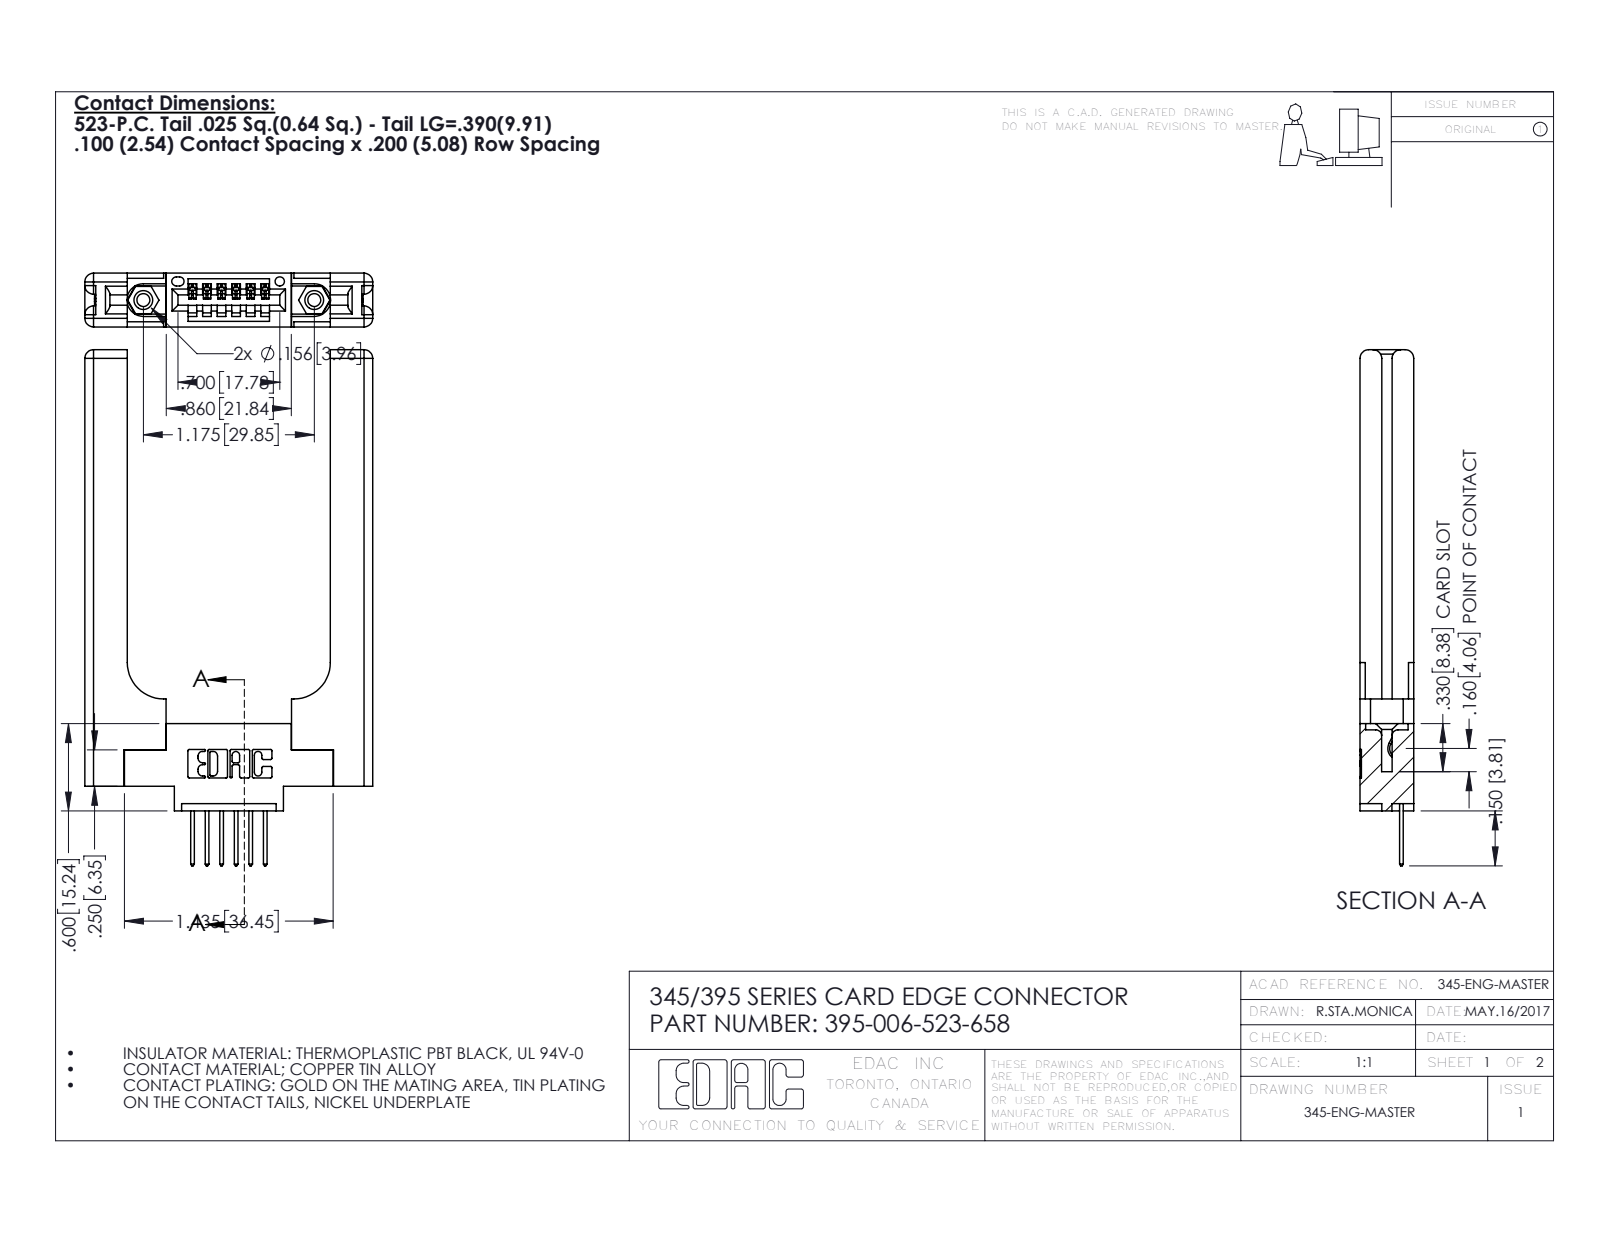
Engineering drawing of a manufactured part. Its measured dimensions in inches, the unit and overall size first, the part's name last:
Units: inches
Overall size (bounding box): 3.547 × 1.979 × 0.37
Round holes (diameter × count): ⌀0.089 ×2, ⌀0.125 ×2, ⌀0.156 ×2, ⌀0.064 ×1
Round bosses / shafts (diameter × count): ⌀0.155 ×2
Partial cylindrical surfaces — rounded edges, fillets, slot ends (radius × count): R0.01 ×22, R0.06 ×16, R0.006 ×12, R0.01 ×12, R0.007 ×6, R0.031 ×6, R0.026 ×3, R0.03 ×2
Main face-to-face distances: 0.37, 0.15, 0.22, 0.072, 0.148, 0.077, 1.396, 0.298, 0.071, 0.292
Hole centre spacings: 0.27, 0.946, 1.175
Volume: 0.785 in³ · Surface area: 16.66 in²
Bodies: 11 solids, 734 faces (472 planar, 202 cylindrical, 60 other)
Part name (STEP PRODUCT): 395-006-523-658; 345 Part_0.170 Offset - 0.156 Dia-TH; 345-220-058_345-220-058; 345-250-001_345-250-001-102 (+1 more)
STEP written by: SolidWorks 2016 (CONFIG_CONTROL_DESIGN)
